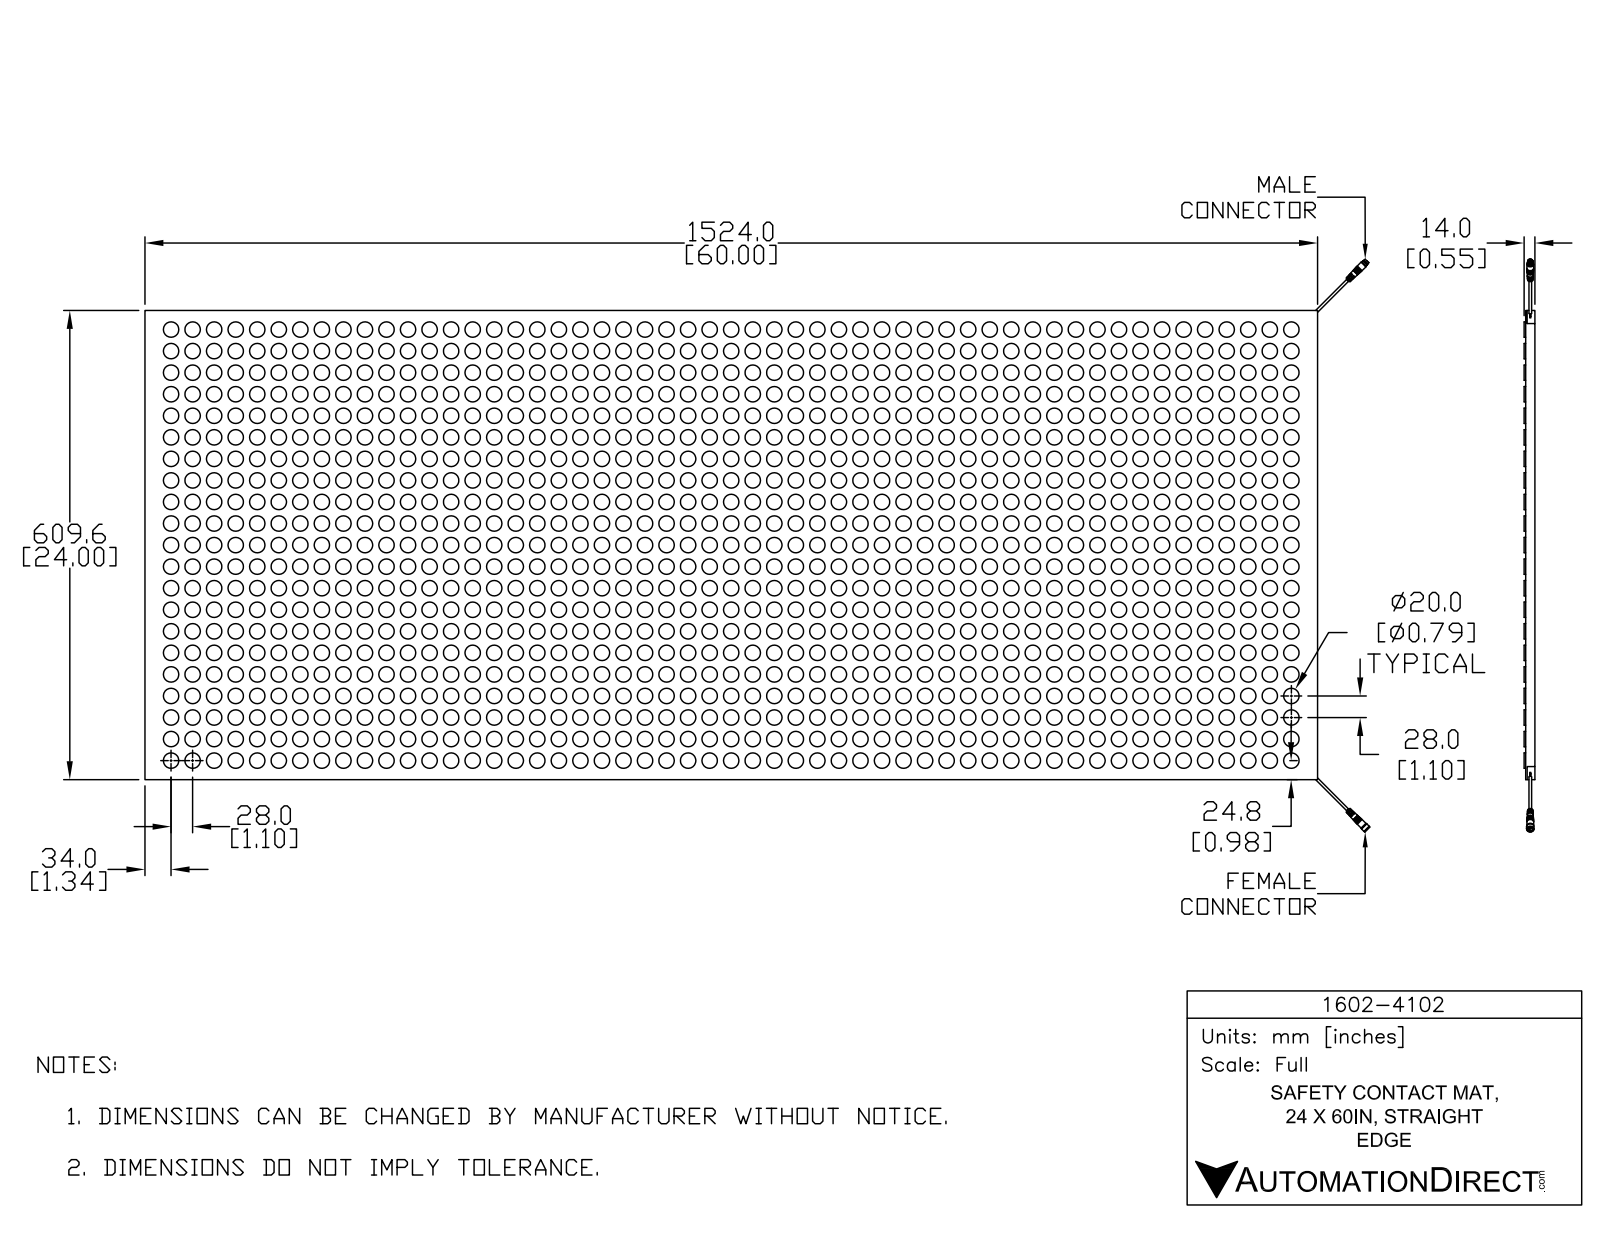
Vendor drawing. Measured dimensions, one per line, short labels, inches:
name: 1602-4102_a
written by: SolidWorks 2018 (AUTOMOTIVE_DESIGN)
unit: in
bodies: 9 solids, 2479 faces (1229 planar, 1168 cylindrical, 82 other)
size: 62.67 × 29.295 × 0.551
volume: 723.1 in³; area: 3 184 in²
holes: 3× ⌀0.063, 2× ⌀0.134, 1× ⌀0.228, 1× ⌀0.232, 1× ⌀0.272, 1× ⌀0.283
bosses: 1113× ⌀0.787, 24× ⌀0.047, 4× ⌀0.031, 3× ⌀0.039, 2× ⌀0.346, 2× ⌀0.138, 1× ⌀0.378, 1× ⌀0.354
face distances: 0.472, 0.079, 0.551, 24, 60, 0.087, 0.394, 0.157, 0.173, 0.047
hole spacings: 0.069, 0.098, 0.138
